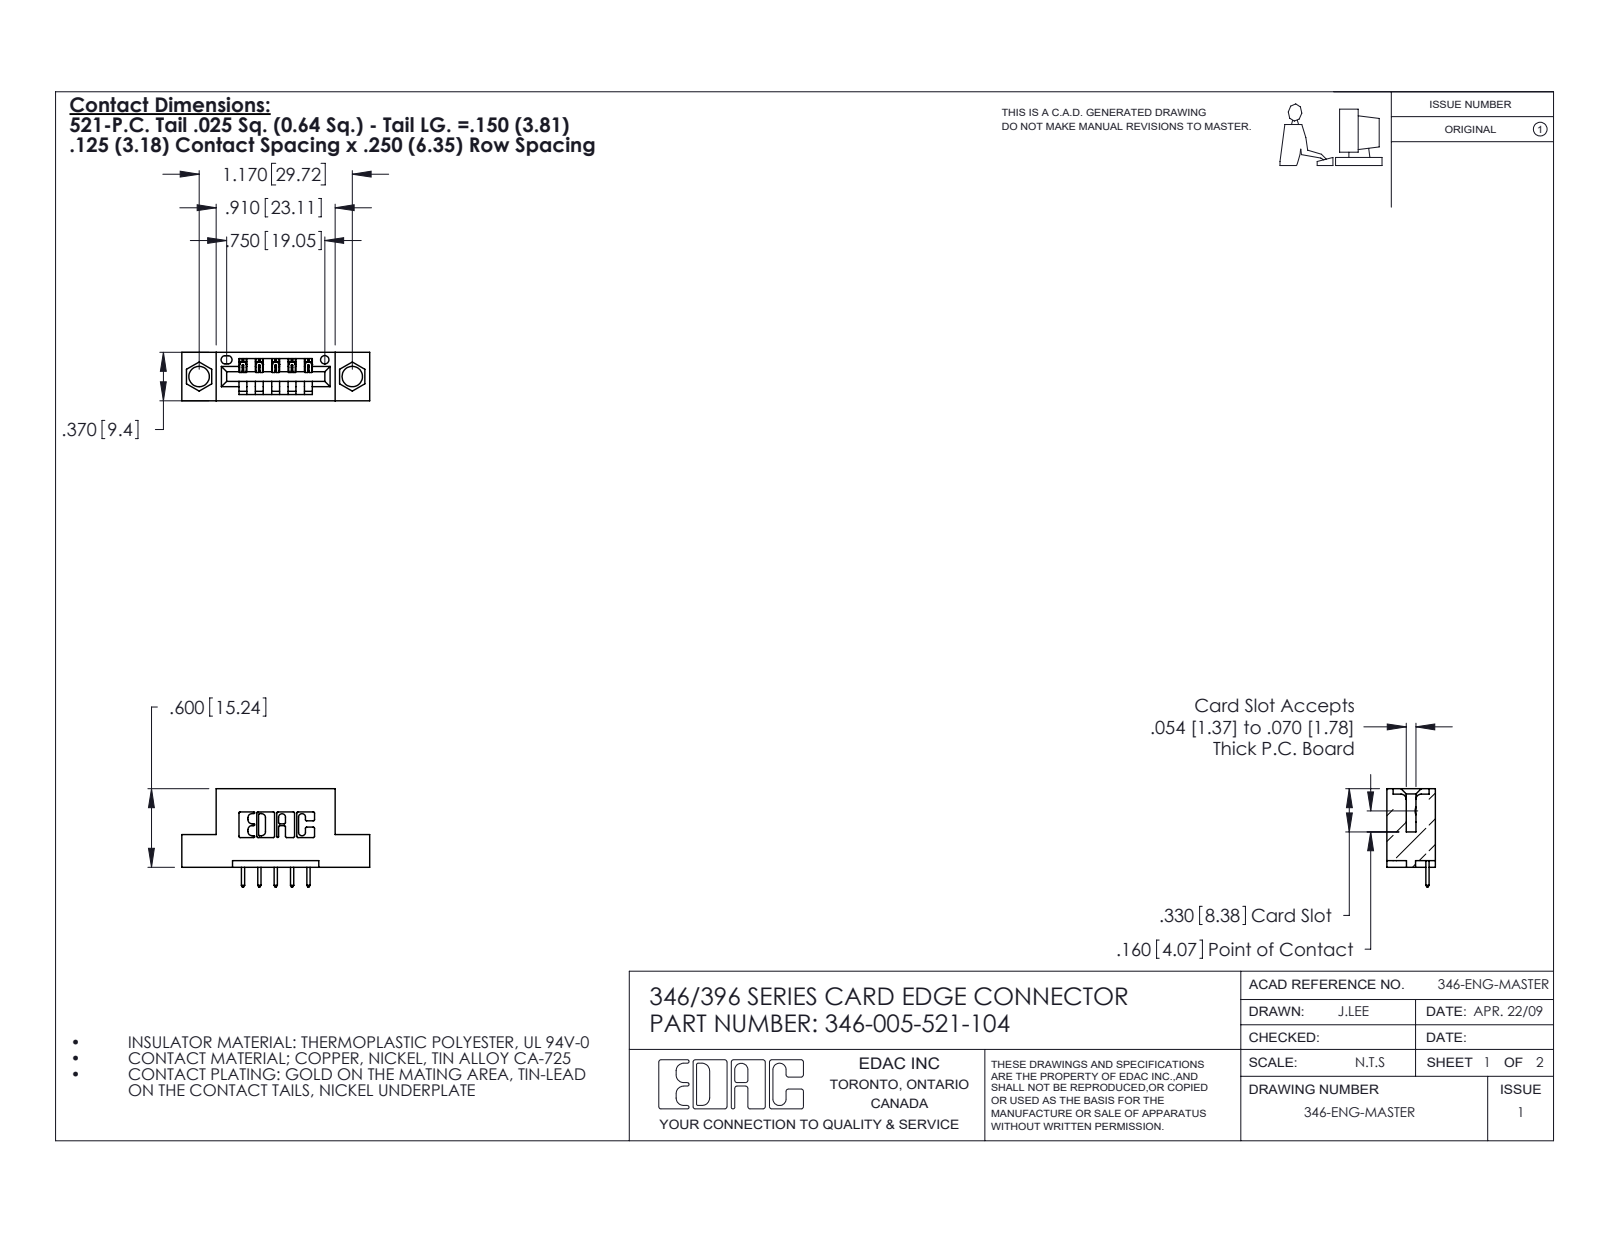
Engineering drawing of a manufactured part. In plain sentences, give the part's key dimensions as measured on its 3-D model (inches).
The part is named "346 Part_Flush Mounting Lugs - 0.156 Dia-TH; 345-292-001_345-293-121; 346-005-521-104". Its 3-D file was written by "SolidWorks 2020 (CONFIG_CONTROL_DESIGN)". It is 6 solids with 426 faces: 290 planar, 136 cylindrical and 0 other. Overall it measures 1.435 by 0.75 by 0.37 inches. Its volume is 0.19 cubic inches and its surface area 5.074 square inches. Round holes: 2 of diameter 0.156, 1 of diameter 0.064. Partial cylindrical surfaces (rounded edges, fillets, slot ends): 22 of radius 0.01, 10 of radius 0.006, 10 of radius 0.01, 6 of radius 0.007, 6 of radius 0.031, 3 of radius 0.026, 2 of radius 0.031, 2 of radius 0.04. The main face-to-face distances are 0.25, 0.37, 0.048, 0.322, 0.148, 0.222, 0.1, 0.174, 0.55, 0.125. The hole center spacings are 0.246, 0.969, 1.17.
